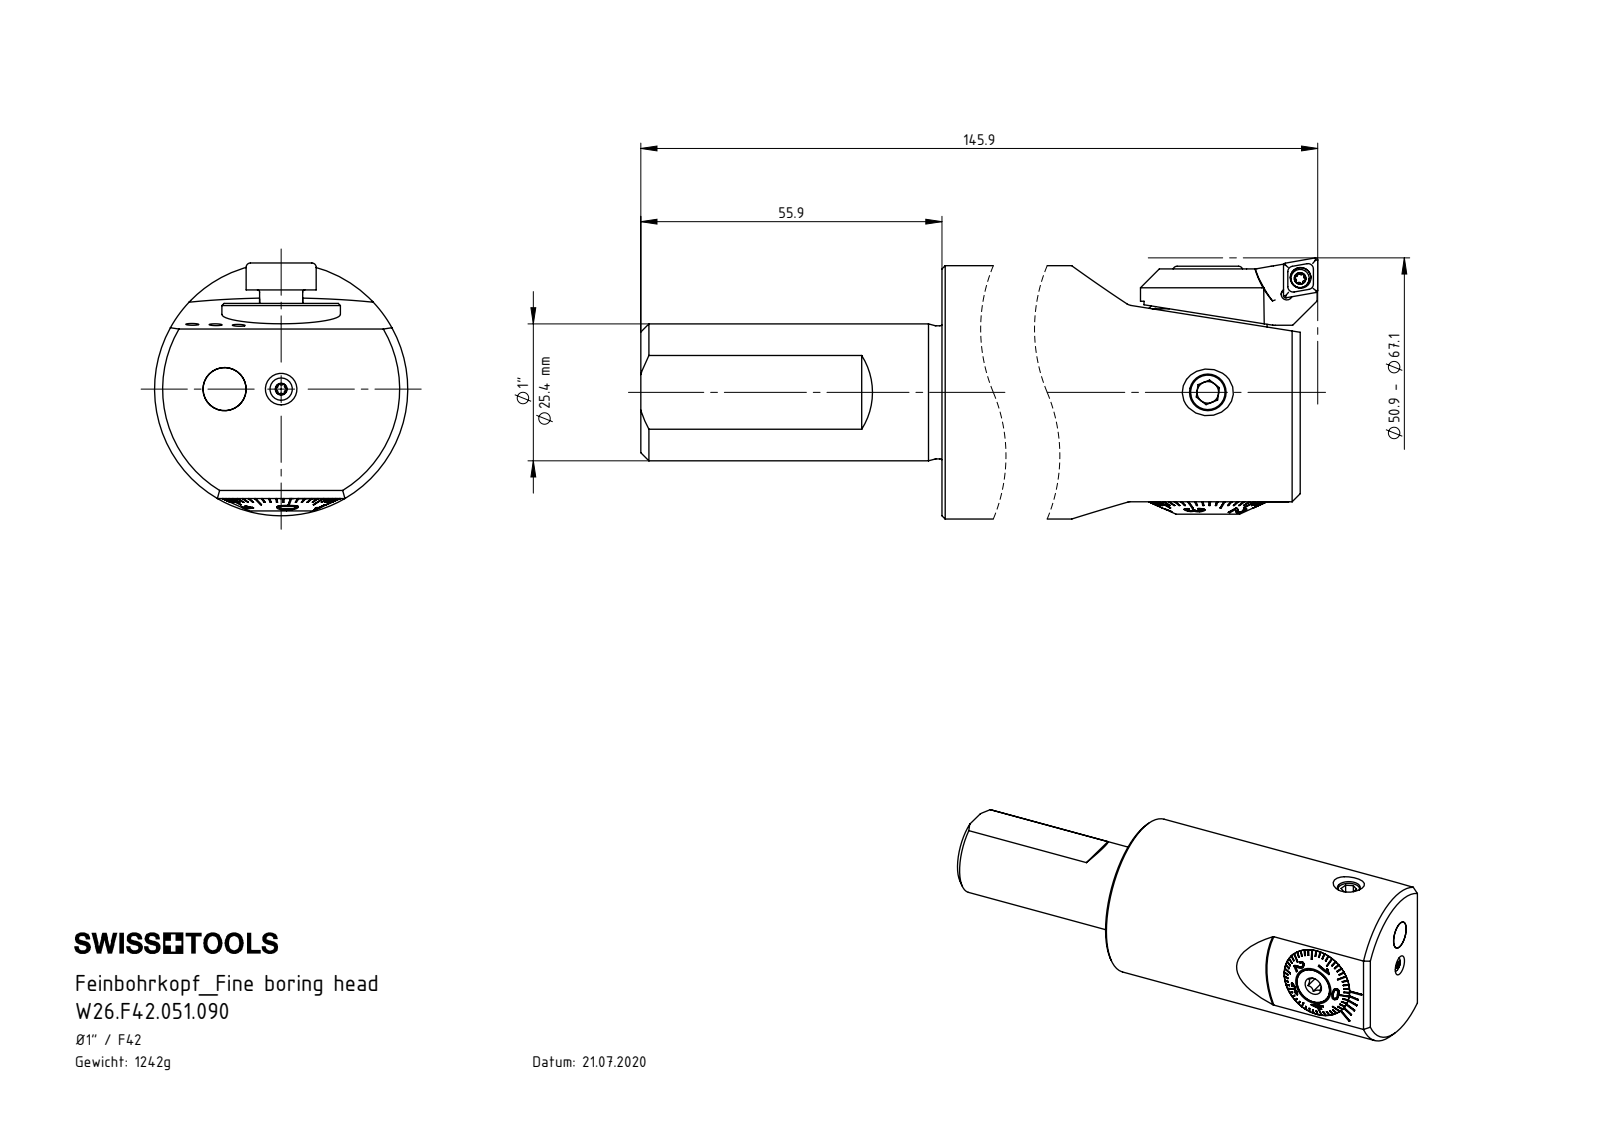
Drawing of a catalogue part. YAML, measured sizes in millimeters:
part_name: "ISO 4026 - M8 x 8_für.step; W26-F42.AA3.090_A_bohrungen gefüllt; F42-BG1.DA3.022_A; DIN 7984 - M8 x 12 (+8 more)"
step_written_by: "SolidWorks 2022 (CONFIG_CONTROL_DESIGN)"
units: millimeters
bodies: {solids: 17, faces: 831, planar: 342, cylindrical: 174, other: 315}
overall_size: [145.9, 48.45, 47]
volume: 159663
surface_area: 39203
round_holes:
  - {diameter: 2.1, count: 4}
  - {diameter: 4.2, count: 2}
  - {diameter: 6.8, count: 2}
  - {diameter: 13.5, count: 2}
  - {diameter: 2.05, count: 1}
  - {diameter: 2.5, count: 1}
  - {diameter: 2.8, count: 1}
  - {diameter: 3, count: 1}
  - {diameter: 3.2, count: 1}
  - {diameter: 3.3, count: 1}
  - {diameter: 3.85, count: 1}
  - {diameter: 3.9, count: 1}
round_bosses_or_shafts:
  - {diameter: 8, count: 2}
  - {diameter: 47, count: 1}
  - {diameter: 25.4, count: 1}
  - {diameter: 24.7, count: 1}
  - {diameter: 21.98, count: 1}
  - {diameter: 21.9, count: 1}
  - {diameter: 18.45, count: 1}
  - {diameter: 13, count: 1}
partial_cylinders:
  - {radius: 0.21, count: 12}
  - {radius: 0.36, count: 9}
  - {radius: 0.5, count: 5}
  - {radius: 1.4, count: 4}
  - {radius: 0.36, count: 3}
  - {radius: 3.2, count: 3}
  - {radius: 2, count: 2}
  - {radius: 2.5, count: 1}
face_to_face_distances: [86.75, 30.6, 4.5, 5.6, 2.2, 36.2, 2.3, 35.1, 1.1, 37.6]
hole_center_spacings: [3.84, 3.99, 10.5, 12.33]
